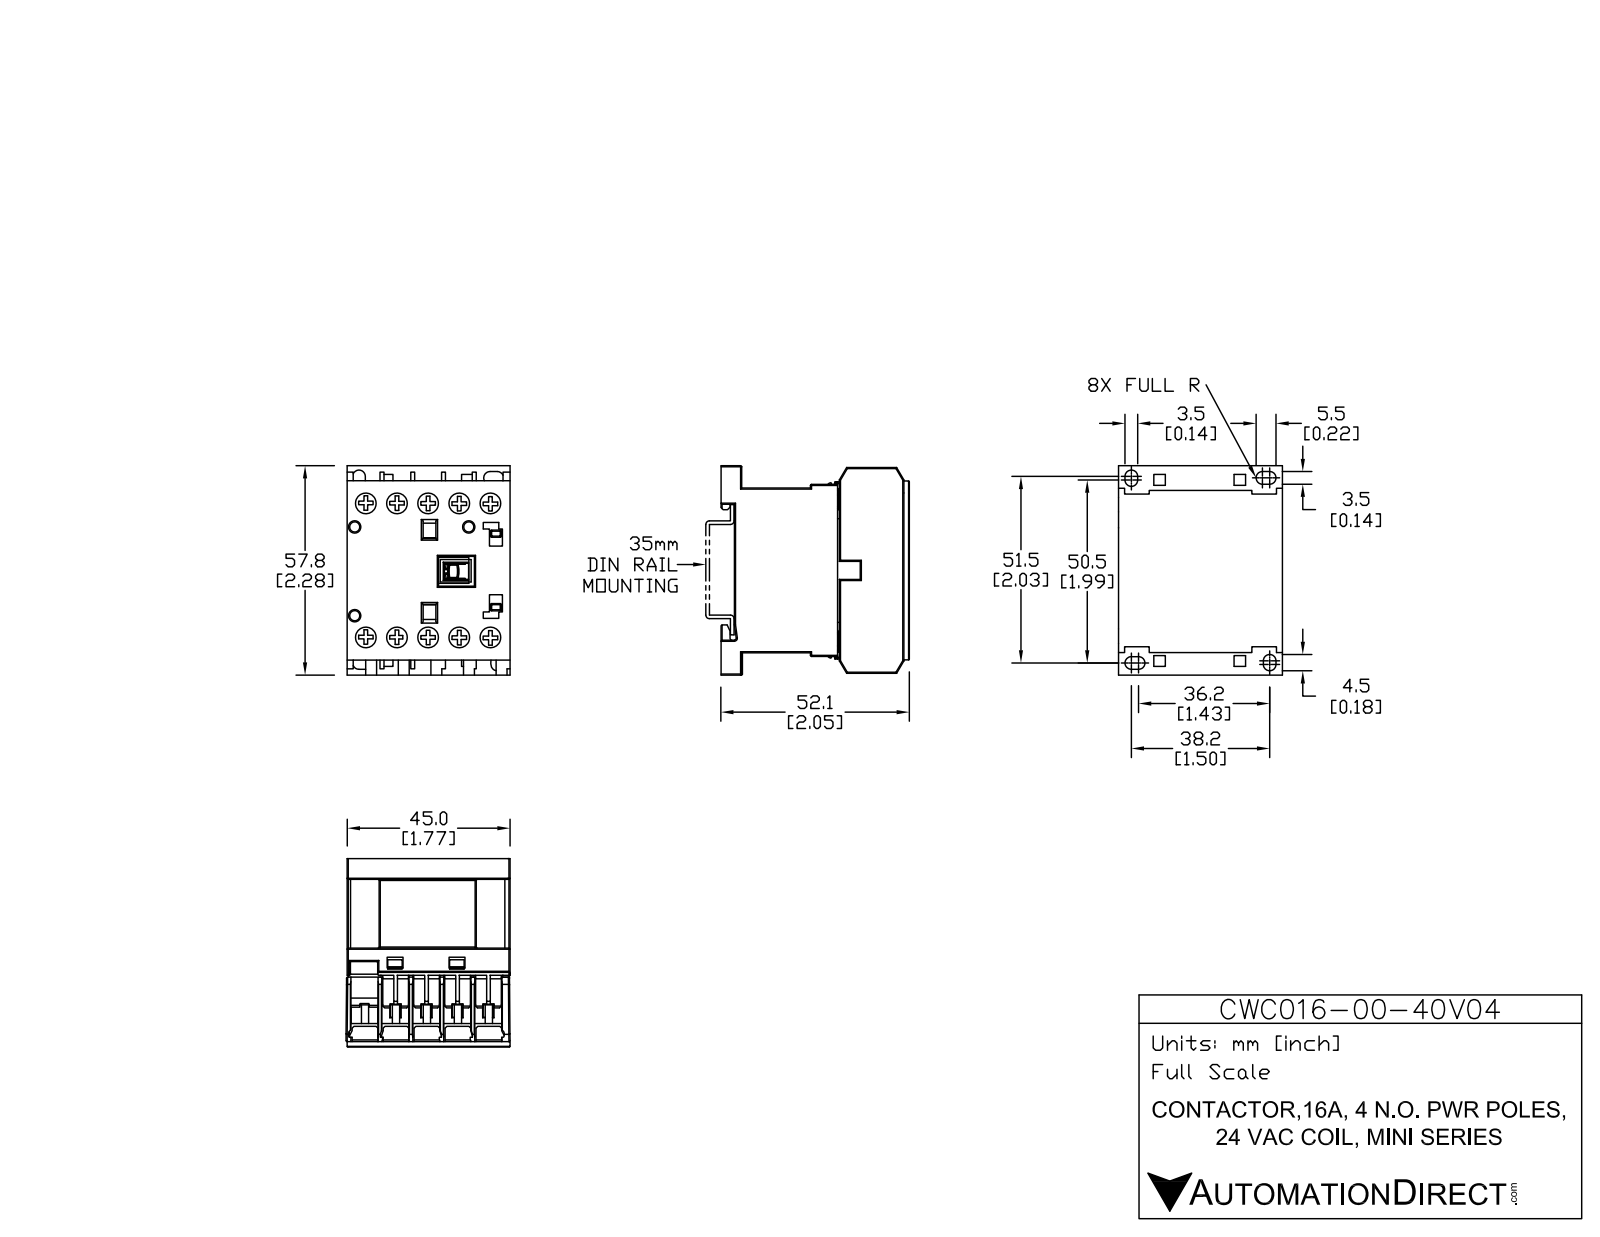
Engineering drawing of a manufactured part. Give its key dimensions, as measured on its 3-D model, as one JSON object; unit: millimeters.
{"part_name": "CWC16-00-40V04", "step_written_by": "SolidWorks 2013 (AUTOMOTIVE_DESIGN)", "units": "millimeters", "bodies": {"solids": 15, "faces": 535, "planar": 445, "cylindrical": 90, "other": 0}, "overall_size": [58.04, 52.12, 45.75], "volume_mm3": 97133, "surface_area_mm2": 30437, "round_holes": [[6.2, 10], [2.8, 3]], "round_bosses_or_shafts": [[5.9, 10]], "partial_cylinders_radius": [[0.3, 20], [1.72, 6], [1.73, 2], [0.32, 1], [0.42, 1], [0.55, 1]], "face_to_face_distances": [8.25, 45.5, 1.25, 16.5, 9.5, 5.5, 17.75, 5.13, 10.63, 7], "hole_center_spacings": [8.55, 37.94, 17.1, 40.72, 36.96, 25.65, 44.99, 6.91]}
